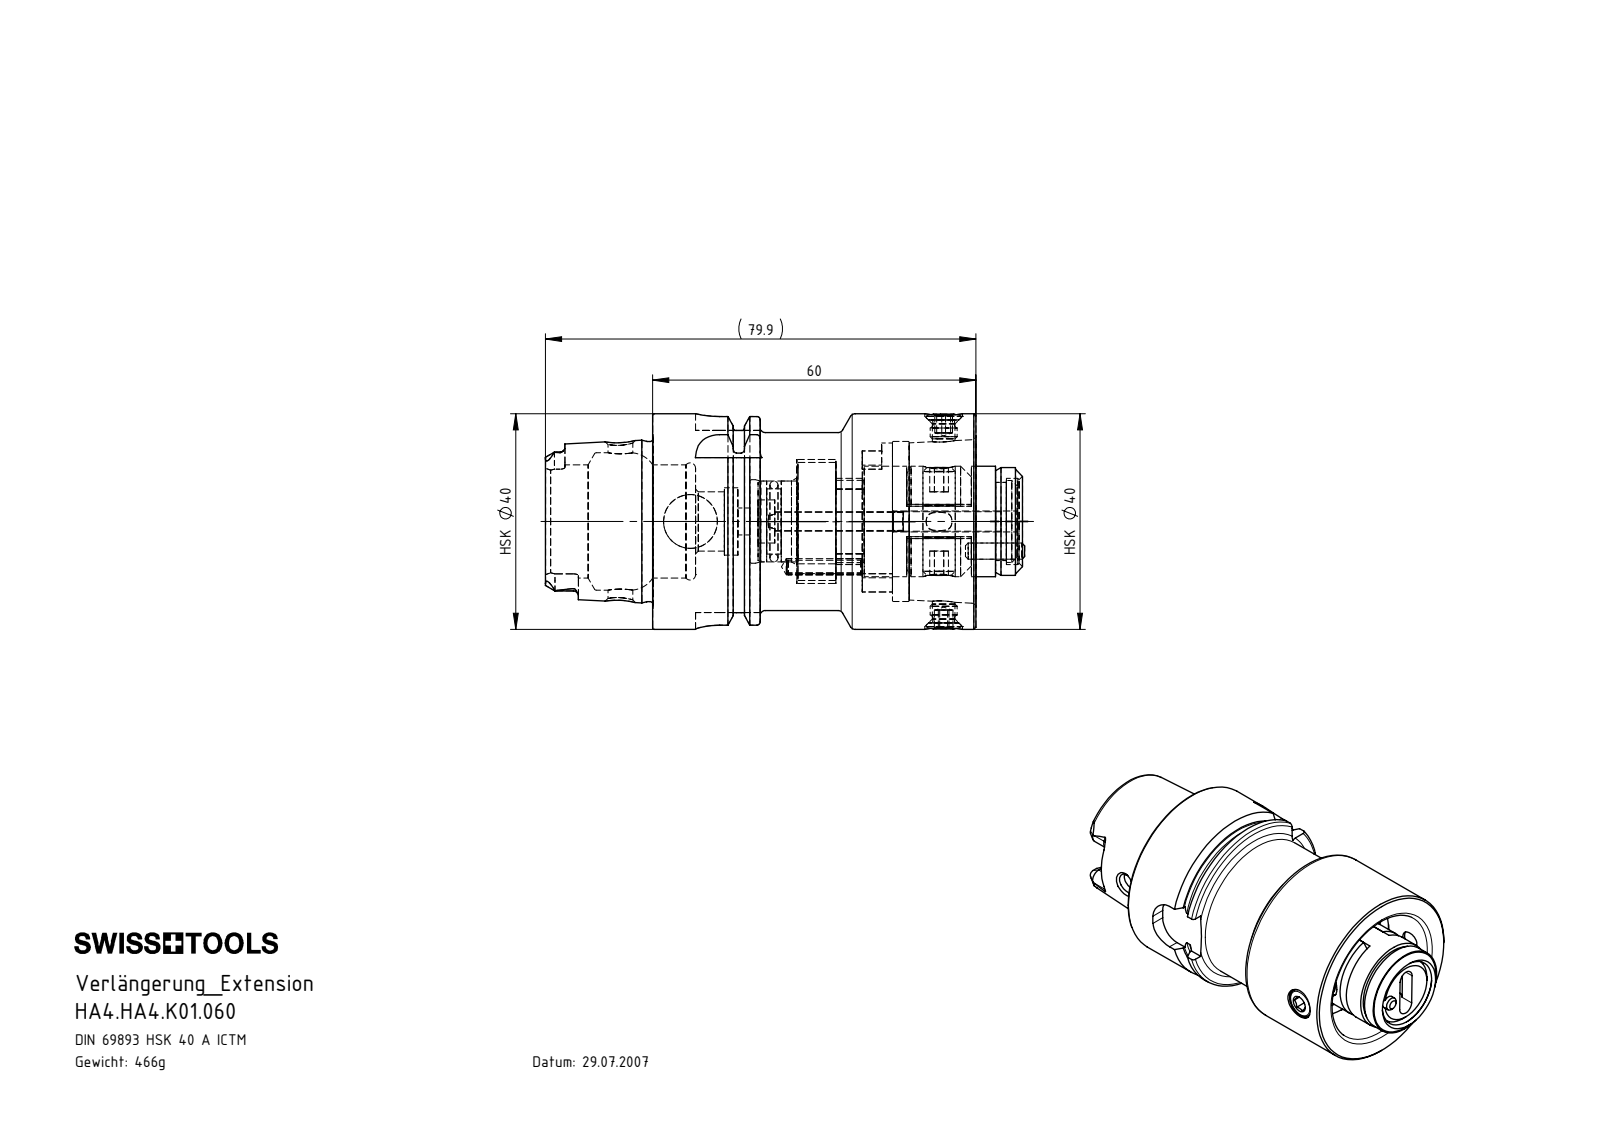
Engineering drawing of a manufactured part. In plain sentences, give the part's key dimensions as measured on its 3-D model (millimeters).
The part is named "HA4-HA4.K01.060; HA4-ER2.001.005_A; ISO 13337 - 3 x 14_Spring Pin ISO 13337 - 3 x 16 - St; HA4-ER1.001.000 (+7 more)". Its 3-D file was written by "SolidWorks 2012 (AUTOMOTIVE_DESIGN)". It is 11 solids with 481 faces: 157 planar, 152 cylindrical and 172 other. Overall it measures 88.95 by 40 by 40 millimeters. Its volume is 59 700 cubic millimeters and its surface area 27 176 square millimeters. Round holes: 2 of diameter 3, 2 of diameter 3.5, 2 of diameter 3.75, 1 of diameter 2.4, 1 of diameter 4.2, 1 of diameter 4.6, 1 of diameter 5, 1 of diameter 6, 1 of diameter 7, 1 of diameter 8, 1 of diameter 10, 1 of diameter 11. Round bosses or shafts: 1 of diameter 40, 1 of diameter 34.75, 1 of diameter 33, 1 of diameter 29.71, 1 of diameter 20.5, 1 of diameter 20, 1 of diameter 15.5, 1 of diameter 15.25. Partial cylindrical surfaces (rounded edges, fillets, slot ends): 8 of radius 1, 6 of radius 0.9, 4 of radius 1.88, 4 of radius 1.95, 4 of radius 2, 4 of radius 4.5, 1 of radius 0.5, 1 of radius 1.5. The main face-to-face distances are 12, 59.15, 12.85, 6, 60, 39.2, 47.15, 38.9, 0.85, 4.5. The hole center spacings are 3.67, 5.5, 6.61, 6.62, 7.34, 7.48, 9.1, 10.93.
